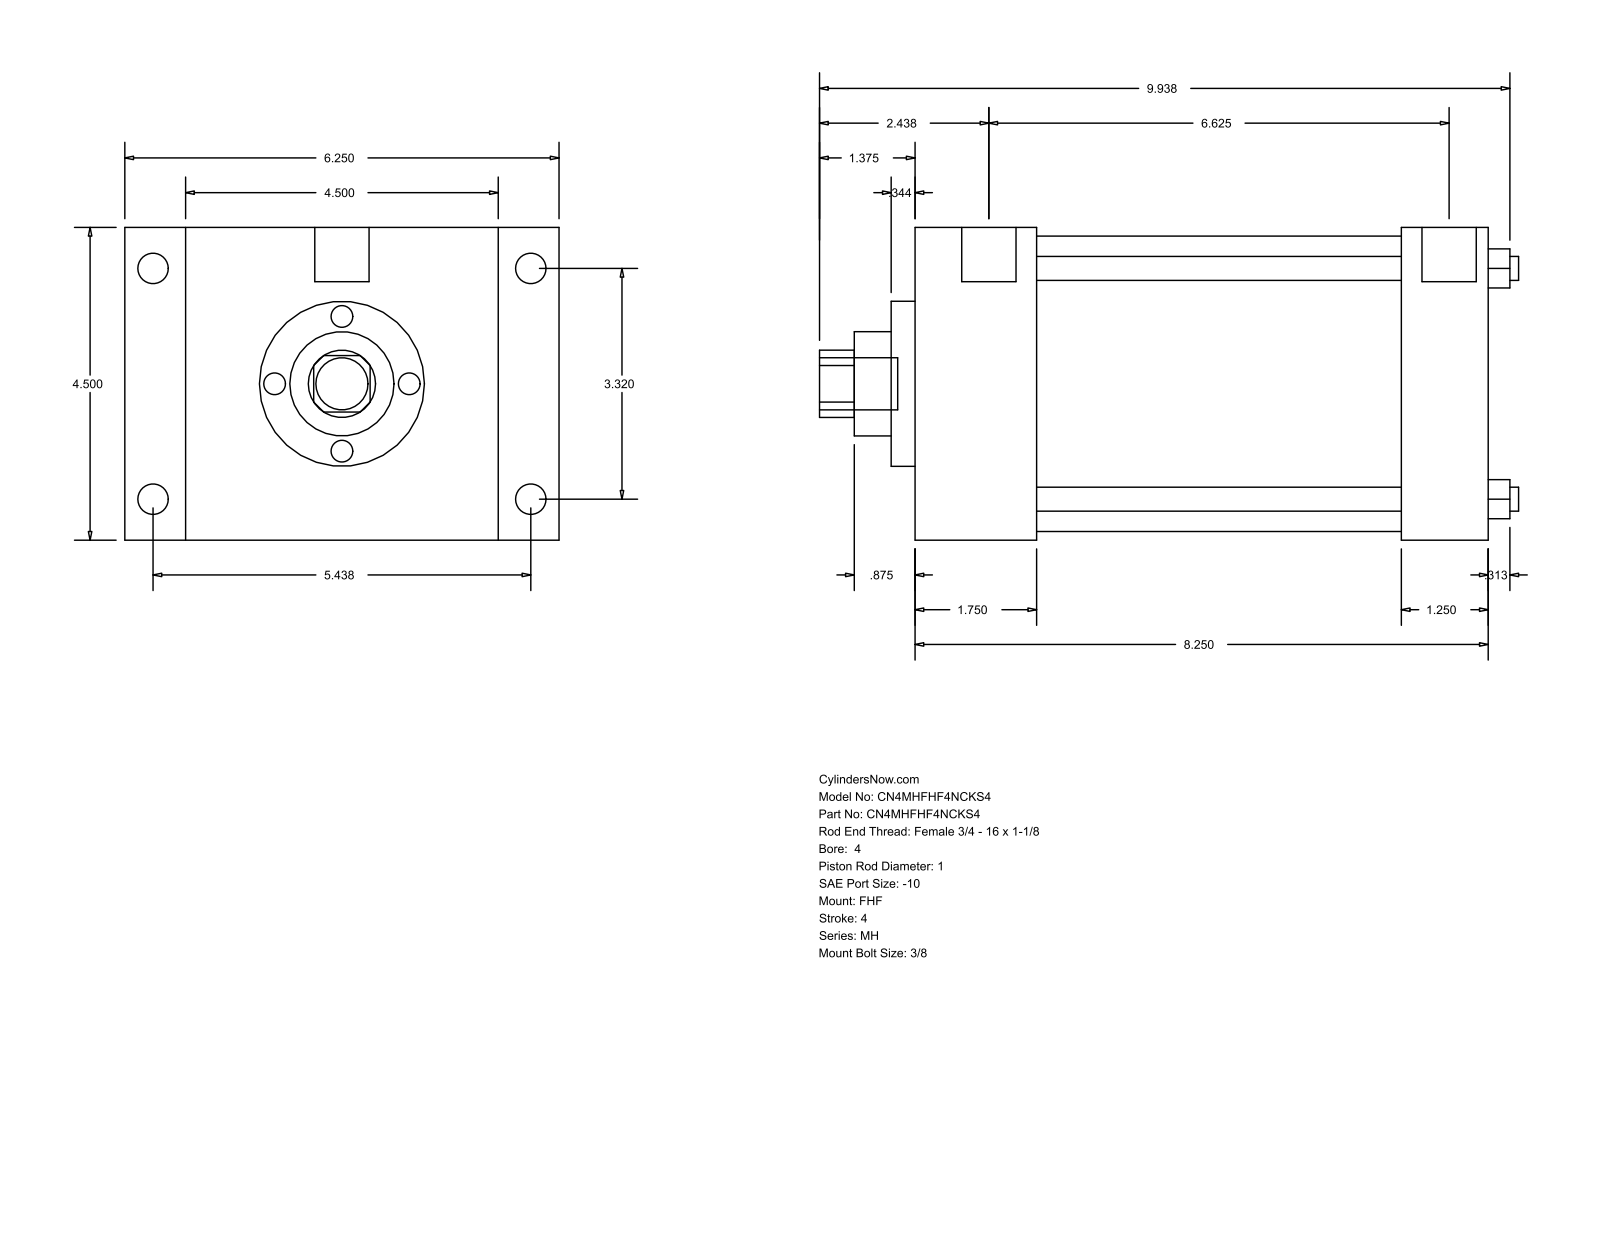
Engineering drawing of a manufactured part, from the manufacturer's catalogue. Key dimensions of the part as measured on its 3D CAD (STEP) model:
Part name (STEP PRODUCT): MH_FHF__0400_1
STEP written by: GSSL Pune (CONFIG_CONTROL_DESIGN)
Units: millimetres
Bodies: 0 solids, 90 faces (61 planar, 29 cylindrical, 0 other)
Overall size (bounding box): 255.59 × 158.75 × 114.3
Round holes (diameter × count): ⌀8.76 ×4, ⌀25.4 ×1, ⌀38.1 ×1, ⌀60.33 ×1, ⌀107.95 ×1
Round bosses / shafts (diameter × count): ⌀11.13 ×4, ⌀8.73 ×4, ⌀19.84 ×2, ⌀19.05 ×1
Partial cylindrical surfaces — rounded edges, fillets, slot ends (radius × count): R12.29 ×1
Main face-to-face distances: 114.3, 209.55, 44.46, 165.09, 22.23, 136.53, 158.76, 177.8, 133.34, 31.75
Hole centre spacings: 59.62, 84.32, 119.25
